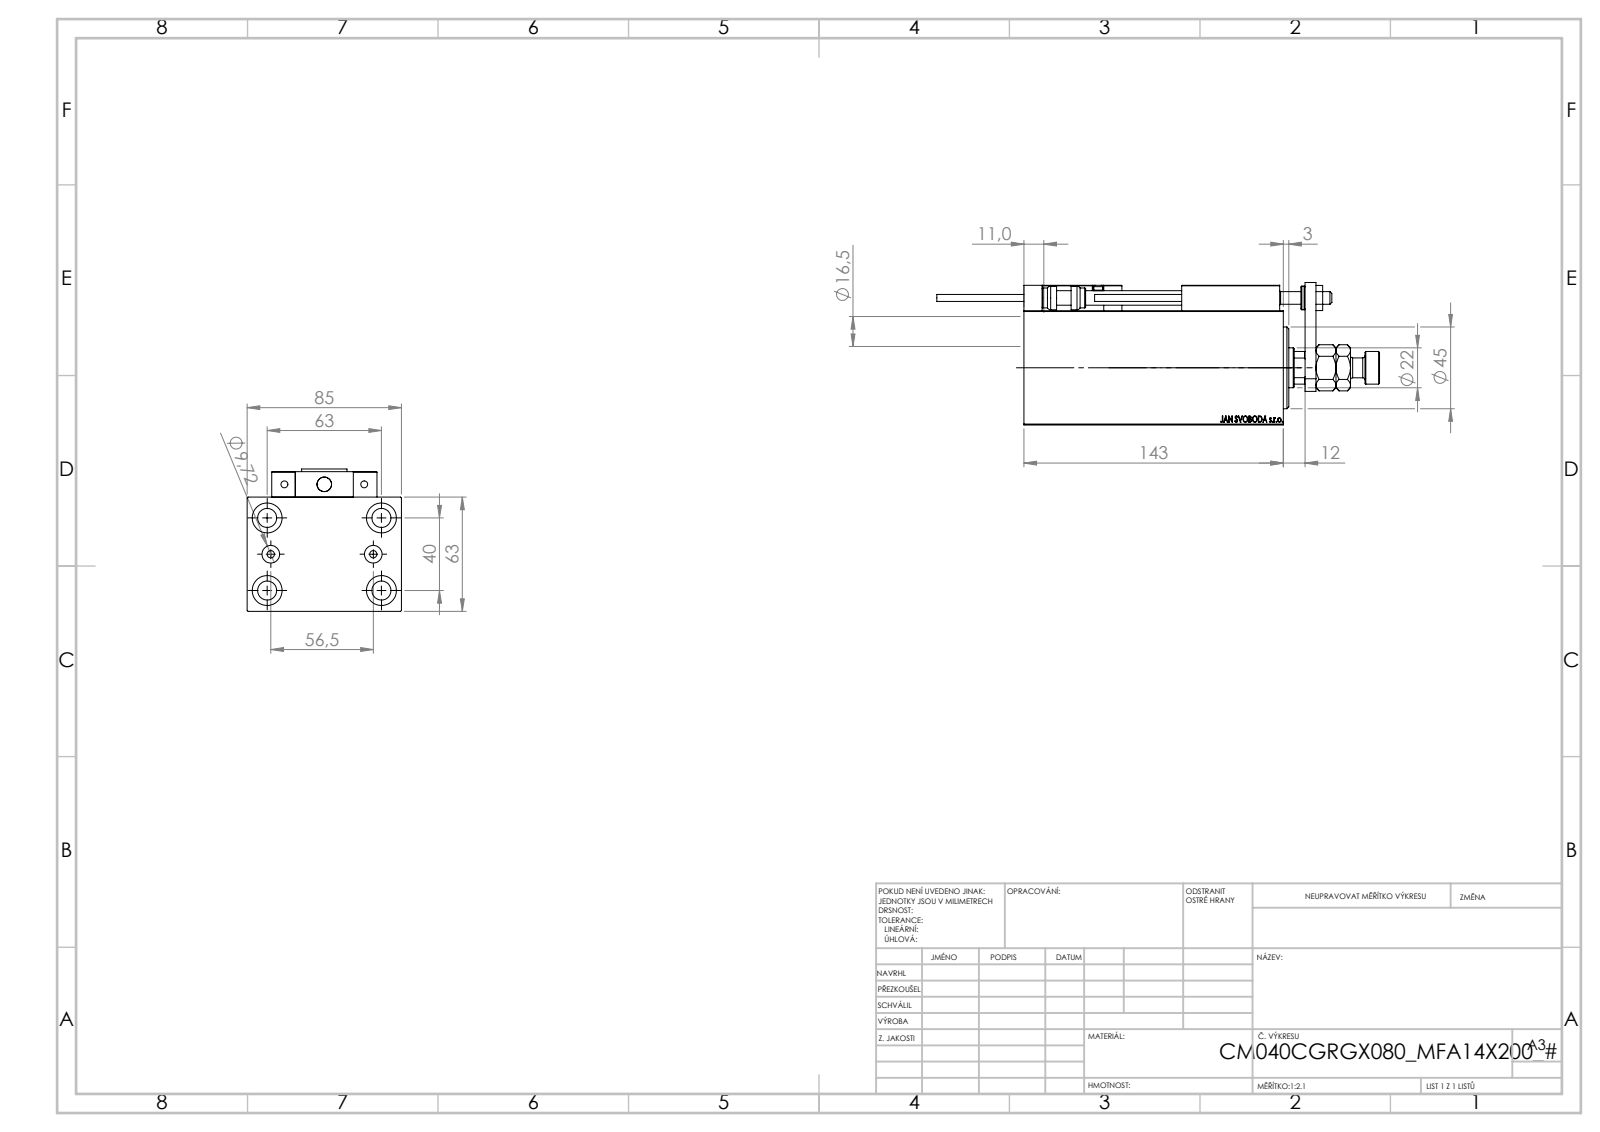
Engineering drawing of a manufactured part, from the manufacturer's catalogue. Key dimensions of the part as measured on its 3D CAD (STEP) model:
Part name (STEP PRODUCT): NUT_D12; SWITCH_X_FRONT_BACK; ALLEN BOLT D5; Block (+8 more)
STEP written by: SolidWorks 2019 (CONFIG_CONTROL_DESIGN)
Units: millimetres
Bodies: 24 solids, 1330 faces (576 planar, 188 cylindrical, 566 other)
Overall size (bounding box): 244 × 85 × 78.5
Volume: 697 176 mm³ · Surface area: 145 709 mm²
Round holes (diameter × count): ⌀4 ×6, ⌀8 ×5, ⌀16.5 ×5, ⌀3.2 ×4, ⌀10.5 ×4, ⌀5 ×2, ⌀9.72 ×2, ⌀7 ×1, ⌀12.5 ×1, ⌀22 ×1, ⌀25.5 ×1, ⌀40 ×1
Round bosses / shafts (diameter × count): ⌀11 ×2, ⌀5 ×2, ⌀3.8 ×2, ⌀18 ×1, ⌀13 ×1
Partial cylindrical surfaces — rounded edges, fillets, slot ends (radius × count): R0.3 ×30, R3 ×2, R10.5 ×1
Main face-to-face distances: 63, 85, 12, 143, 131, 14, 18, 77, 20, 6
Hole centre spacings: 20.26, 37.31, 63.01, 11.37, 20, 28.25, 29.59, 29.69
